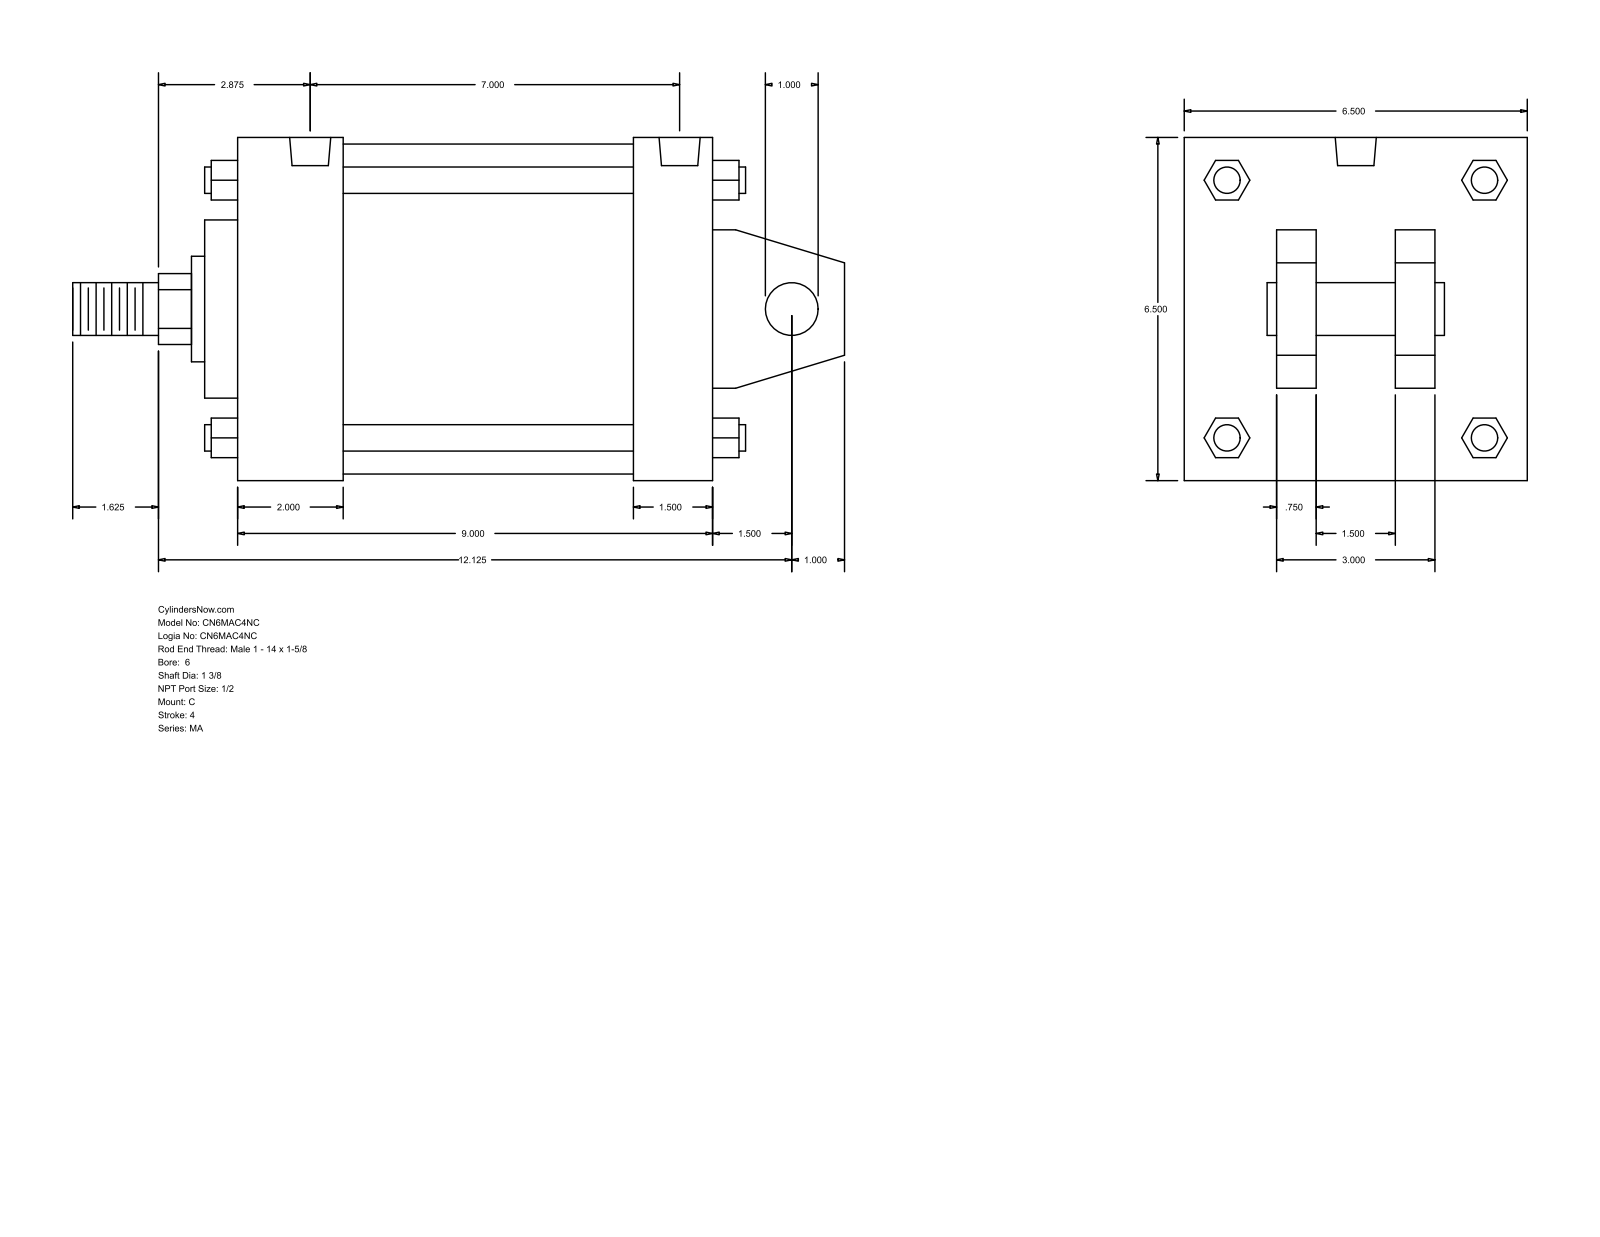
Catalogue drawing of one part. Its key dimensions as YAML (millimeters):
part_name: "MA_C__0600_1.375"
step_written_by: "GSSL Pune (CONFIG_CONTROL_DESIGN)"
units: millimeters
bodies: {solids: 0, faces: 141, planar: 109, cylindrical: 32, other: 0}
overall_size: [371.48, 165.1, 165.1]
round_holes:
  - {diameter: 17.46, count: 4}
  - {diameter: 19.77, count: 2}
round_bosses_or_shafts:
  - {diameter: 12.7, count: 4}
  - {diameter: 25.4, count: 2}
  - {diameter: 158.75, count: 1}
  - {diameter: 85.72, count: 1}
  - {diameter: 50.8, count: 1}
  - {diameter: 34.92, count: 1}
partial_cylinders:
  - {radius: 17.06, count: 1}
face_to_face_distances: [165.1, 228.6, 38.1, 19.05, 63.5, 101.6, 50.8, 120.65, 44.45, 190.5]
hole_center_spacings: [177.8, 3.17, 3.18, 174.62, 177.79, 180.97]
